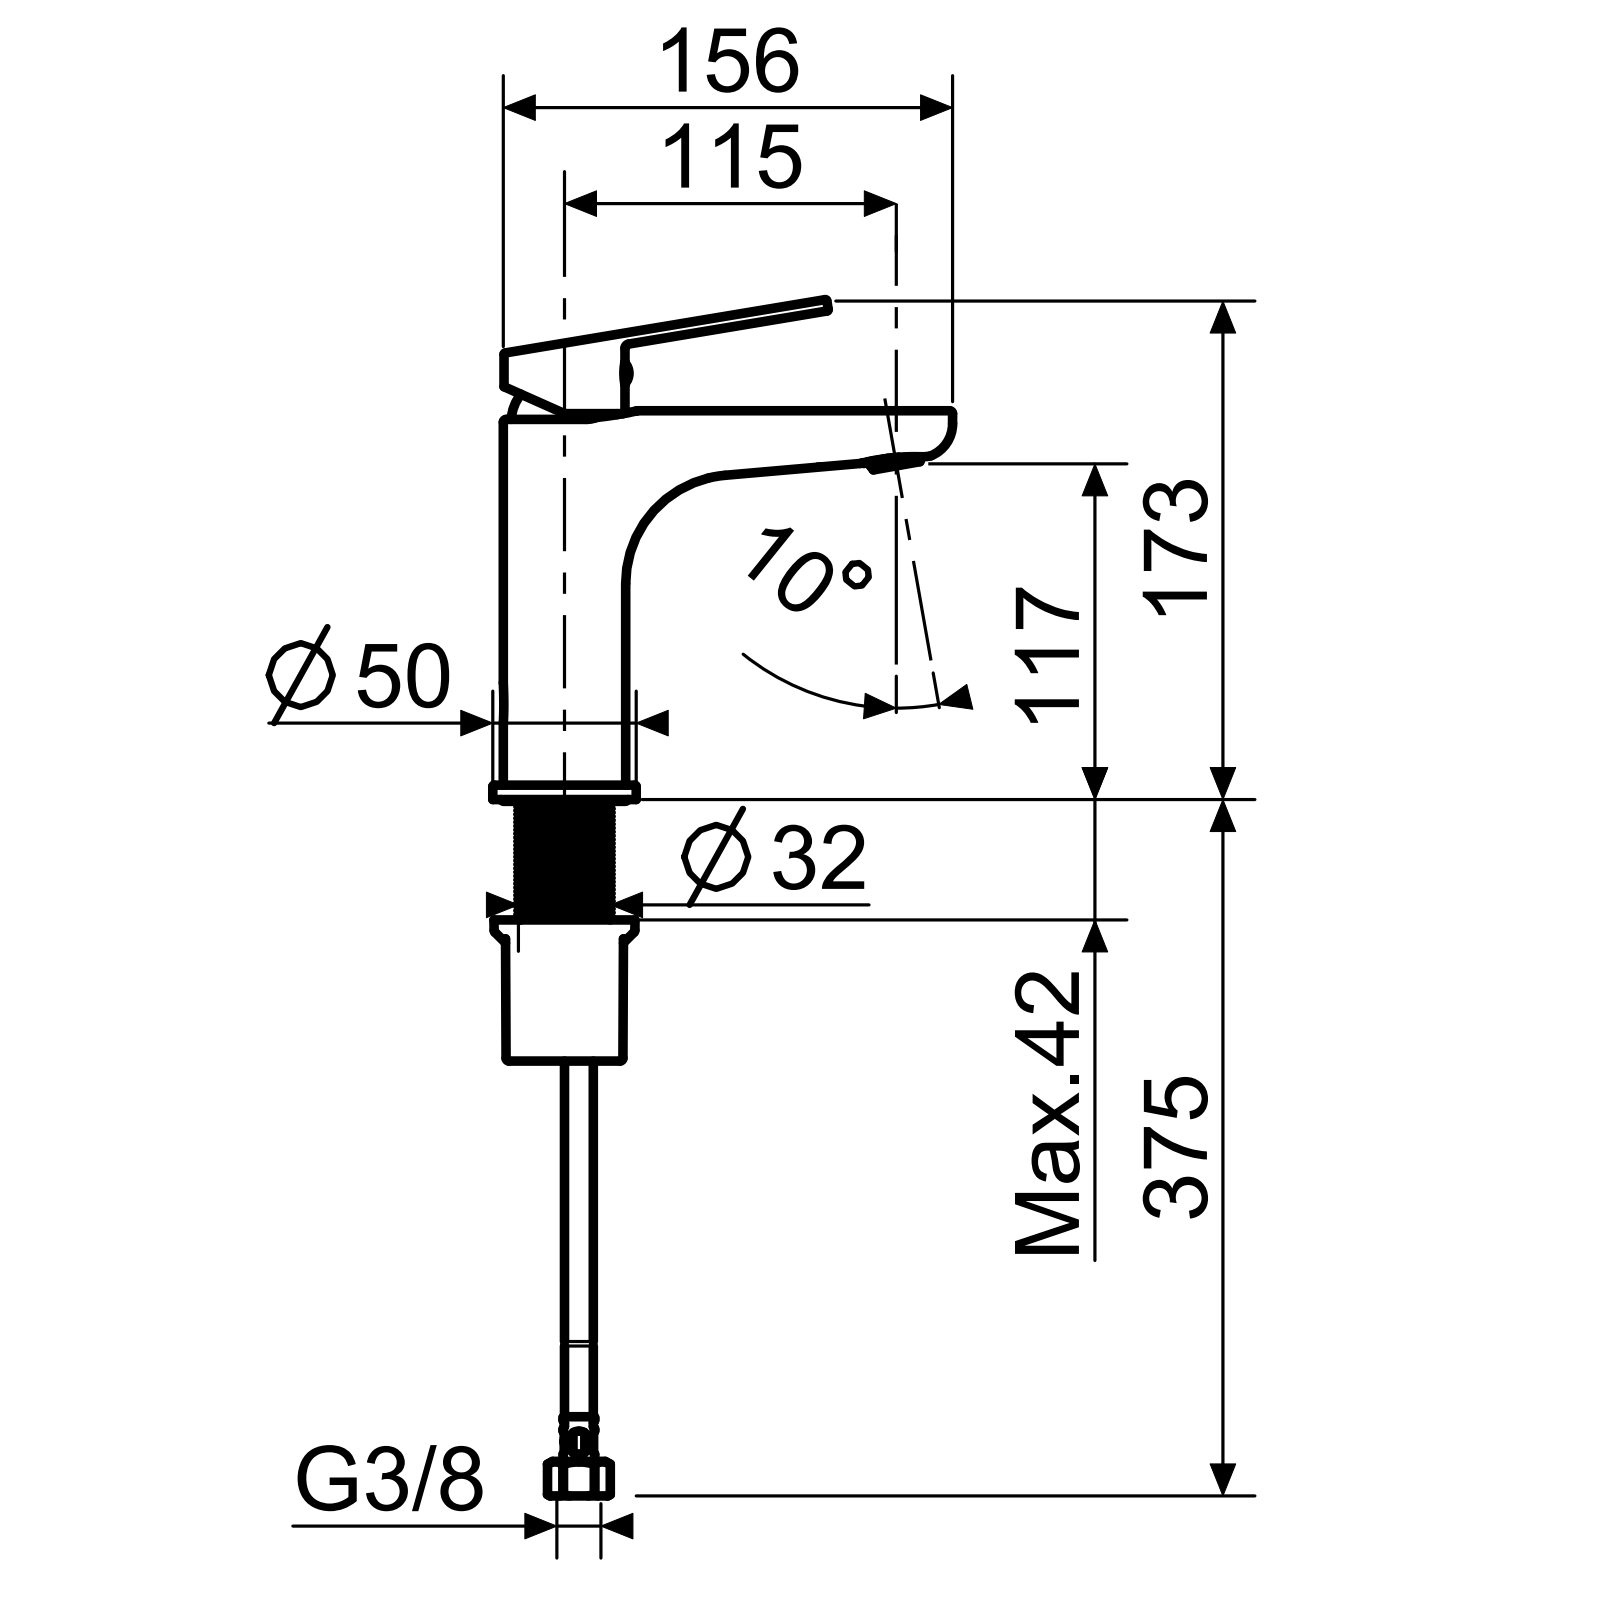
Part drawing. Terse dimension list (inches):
name: ATAO200C001; SCCMAC0011; ATAO005C001; SPLMAC0005 (+3 more)
written by: CREO PARAMETRIC BY PTC INC, 2022164 (CONFIG_CONTROL_DESIGN)
unit: in
bodies: 6 solids, 2800 faces (1816 planar, 784 cylindrical, 200 other)
size: 6.834 × 6.481 × 3.15
volume: 18.67 in³; area: 121.6 in²
holes: 317× ⌀0.02, 2× ⌀0.315, 1× ⌀0.165, 1× ⌀0.197, 1× ⌀0.217, 1× ⌀0.256, 1× ⌀0.63, 1× ⌀0.701, 1× ⌀0.866, 1× ⌀0.906, 1× ⌀0.965, 1× ⌀1.091
bosses: 1× ⌀1.961, 1× ⌀1.673, 1× ⌀1.654, 1× ⌀1.575, 1× ⌀1.496, 1× ⌀1.449, 1× ⌀0.937, 1× ⌀0.886
rounds: 23× R0.02, 16× R0.004, 6× R0.039, 6× R0.063, 4× R0.118, 2× R0.059, 2× R0.374, 2× R6.97
face distances: 1.673, 5, 5.197, 0.197, 0.079, 0.118, 5.118, 0.658, 1.015, 0.244
hole spacings: 0.303, 0.303, 0.063, 0.126, 0.187, 0.246, 0.356, 0.111
